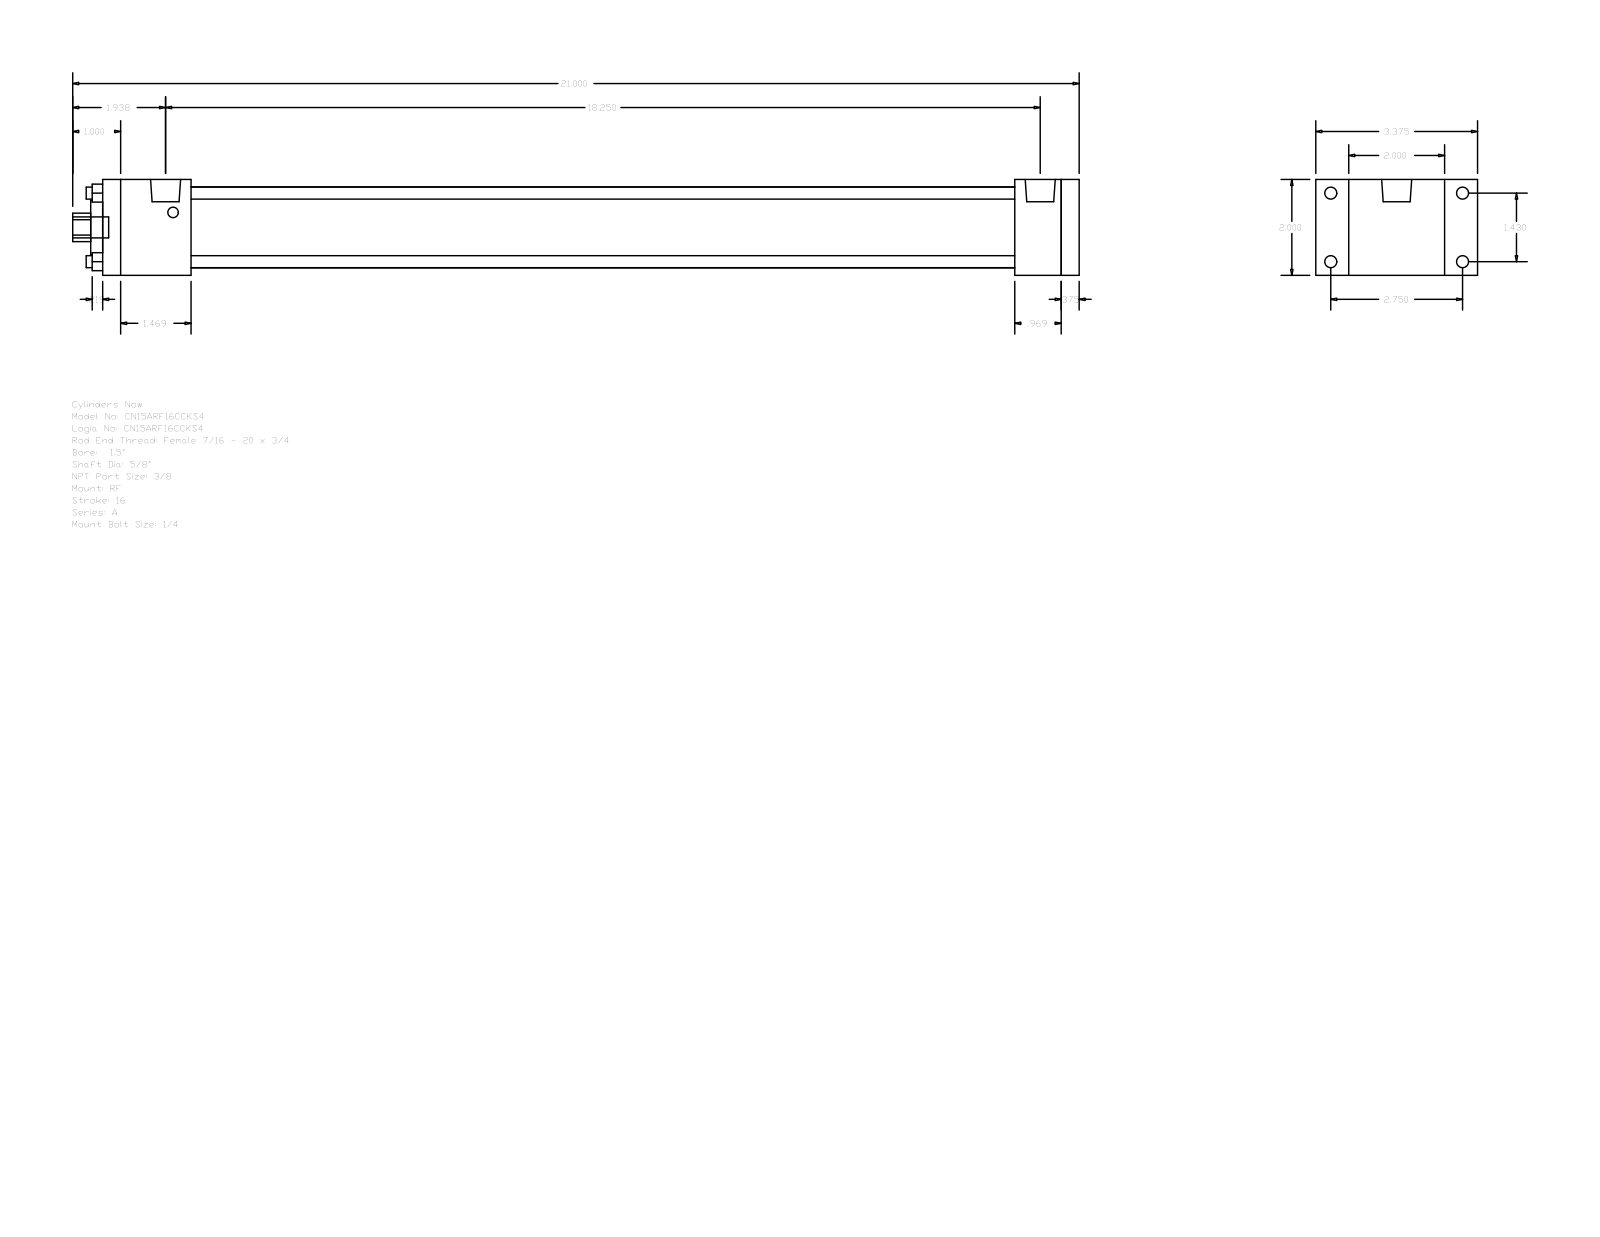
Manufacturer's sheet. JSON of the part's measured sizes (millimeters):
{"part_name": "A_RF__0150_0.625", "step_written_by": "GSSL Pune (CONFIG_CONTROL_DESIGN)", "units": "millimeters", "bodies": {"solids": 0, "faces": 92, "planar": 64, "cylindrical": 28, "other": 0}, "overall_size": [533.4, 85.72, 50.8], "round_holes": [[6.35, 4], [15.88, 1], [28.57, 1], [42.93, 1]], "round_bosses_or_shafts": [[6.35, 4], [5.56, 4], [15.93, 2], [11.11, 1]], "partial_cylinders_radius": [[7.54, 1]], "face_to_face_distances": [50.8, 9.52, 508, 517.52, 483.39, 24.61, 34.13, 46.83, 436.56, 461.17], "hole_center_spacings": [25.68, 36.32, 51.36]}
